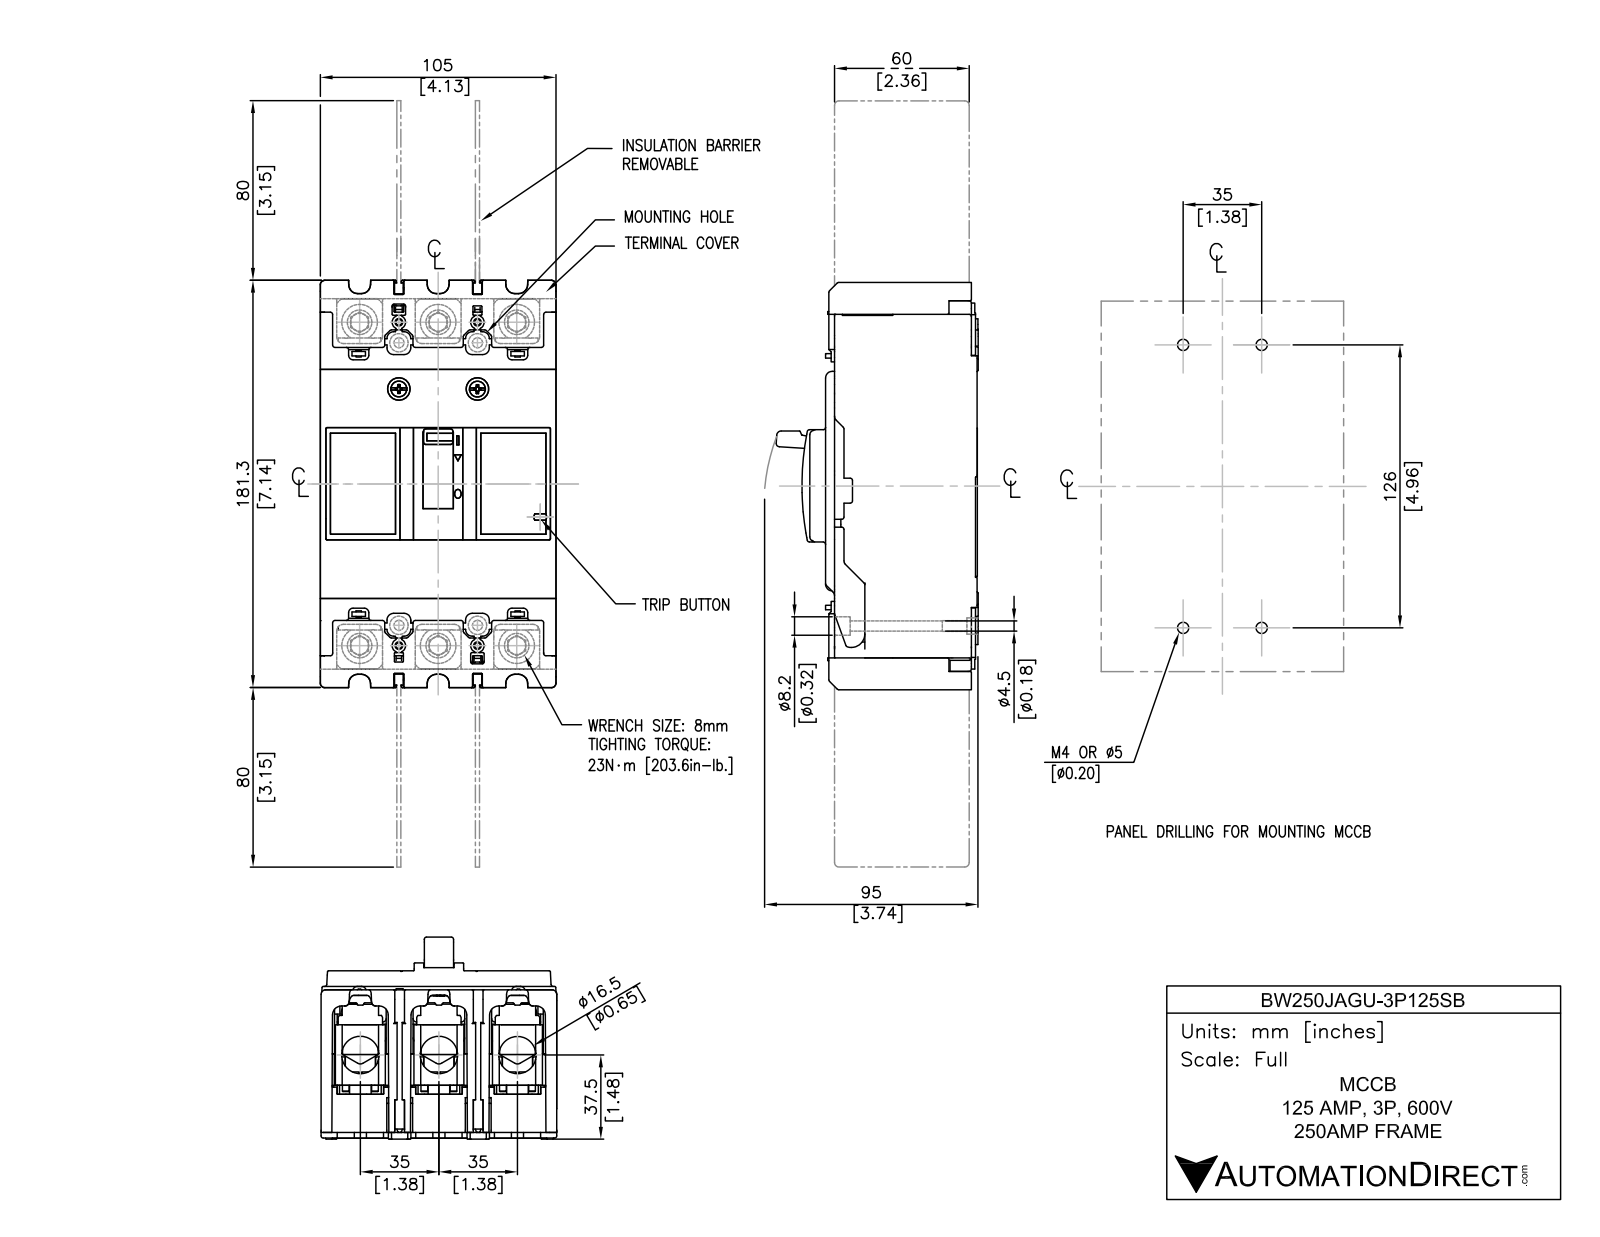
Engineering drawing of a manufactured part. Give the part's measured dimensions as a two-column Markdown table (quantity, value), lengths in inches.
| quantity | value |
| --- | --- |
| part name | BW250JAGU-3P125SB |
| STEP written by | SolidWorks 2018 (AUTOMOTIVE_DESIGN) |
| units | inches |
| bodies | 10 solids, 471 faces (338 planar, 121 cylindrical, 12 other) |
| overall size | 7.441 × 4.134 × 3.583 |
| volume | 67.56 in³ |
| surface area | 224 in² |
| round holes (diameter × count) | 0.315 × 6, 0.177 × 4, 0.323 × 4 |
| round bosses / shafts (diameter × count) | 0.512 × 6 |
| partial cylindrical surfaces (radius × count) | 0.039 × 36, 0.118 × 16, 0.079 × 8, 0.492 × 3 |
| main face-to-face distances | 0.098, 2.5, 4.134, 1.378, 0.787, 2.598, 1.24, 0.335, 0.157, 0.059 |
| hole center spacings | 0.775, 5.359, 1.378, 2.097, 5.703, 5.834, 5.669, 2.756 |
